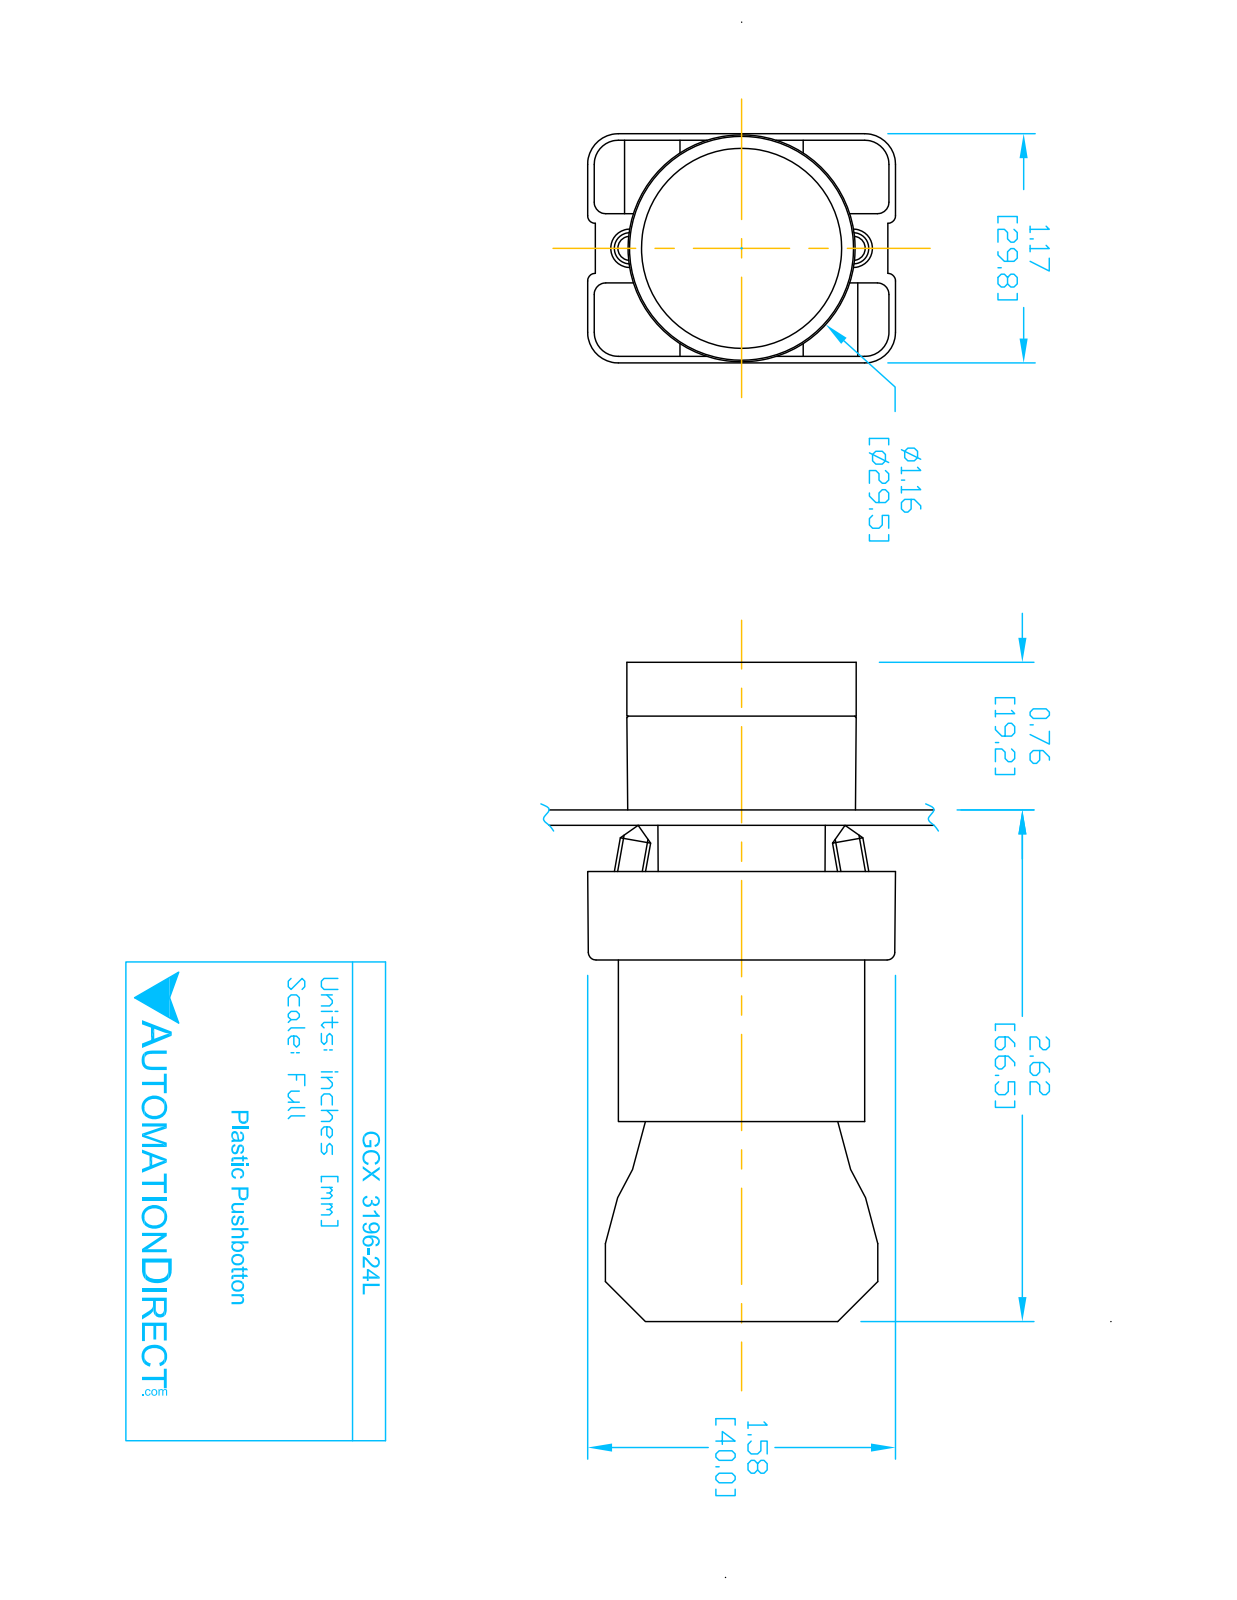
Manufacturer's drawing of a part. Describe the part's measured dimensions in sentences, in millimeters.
The part is named "ECX3029-2; GCX3196-24L; CONTACT BLOCK; GCX3196L OPERATOR (+1 more)". Its 3-D file was written by "SolidWorks 2016 (AUTOMOTIVE_DESIGN)". It is 8 solids with 431 faces: 252 planar, 148 cylindrical and 31 other. Overall it measures 84.3 by 40.2 by 29.9 millimeters. Its volume is 45 790 cubic millimeters and its surface area 25 010 square millimeters. Round holes: 2 of diameter 2, 2 of diameter 3.1, 2 of diameter 3.3, 1 of diameter 2.2, 1 of diameter 5, 1 of diameter 11.9, 1 of diameter 22.3, 1 of diameter 22.6, 1 of diameter 26. Round bosses or shafts: 4 of diameter 4, 1 of diameter 29.8, 1 of diameter 25.5, 1 of diameter 24, 1 of diameter 21.7, 1 of diameter 19.8, 1 of diameter 12.8. Partial cylindrical surfaces (rounded edges, fillets, slot ends): 24 of radius 1.5, 12 of radius 1, 12 of radius 3.1, 12 of radius 4, 8 of radius 1, 2 of radius 3.3, 1 of radius 0.5, 1 of radius 1.6. The main face-to-face distances are 21, 14.7, 51.3, 30.3, 29.7, 7, 58.3, 37.3, 0.8, 0.8. The hole center spacings are 6, 13.8, 12, 12.4.
